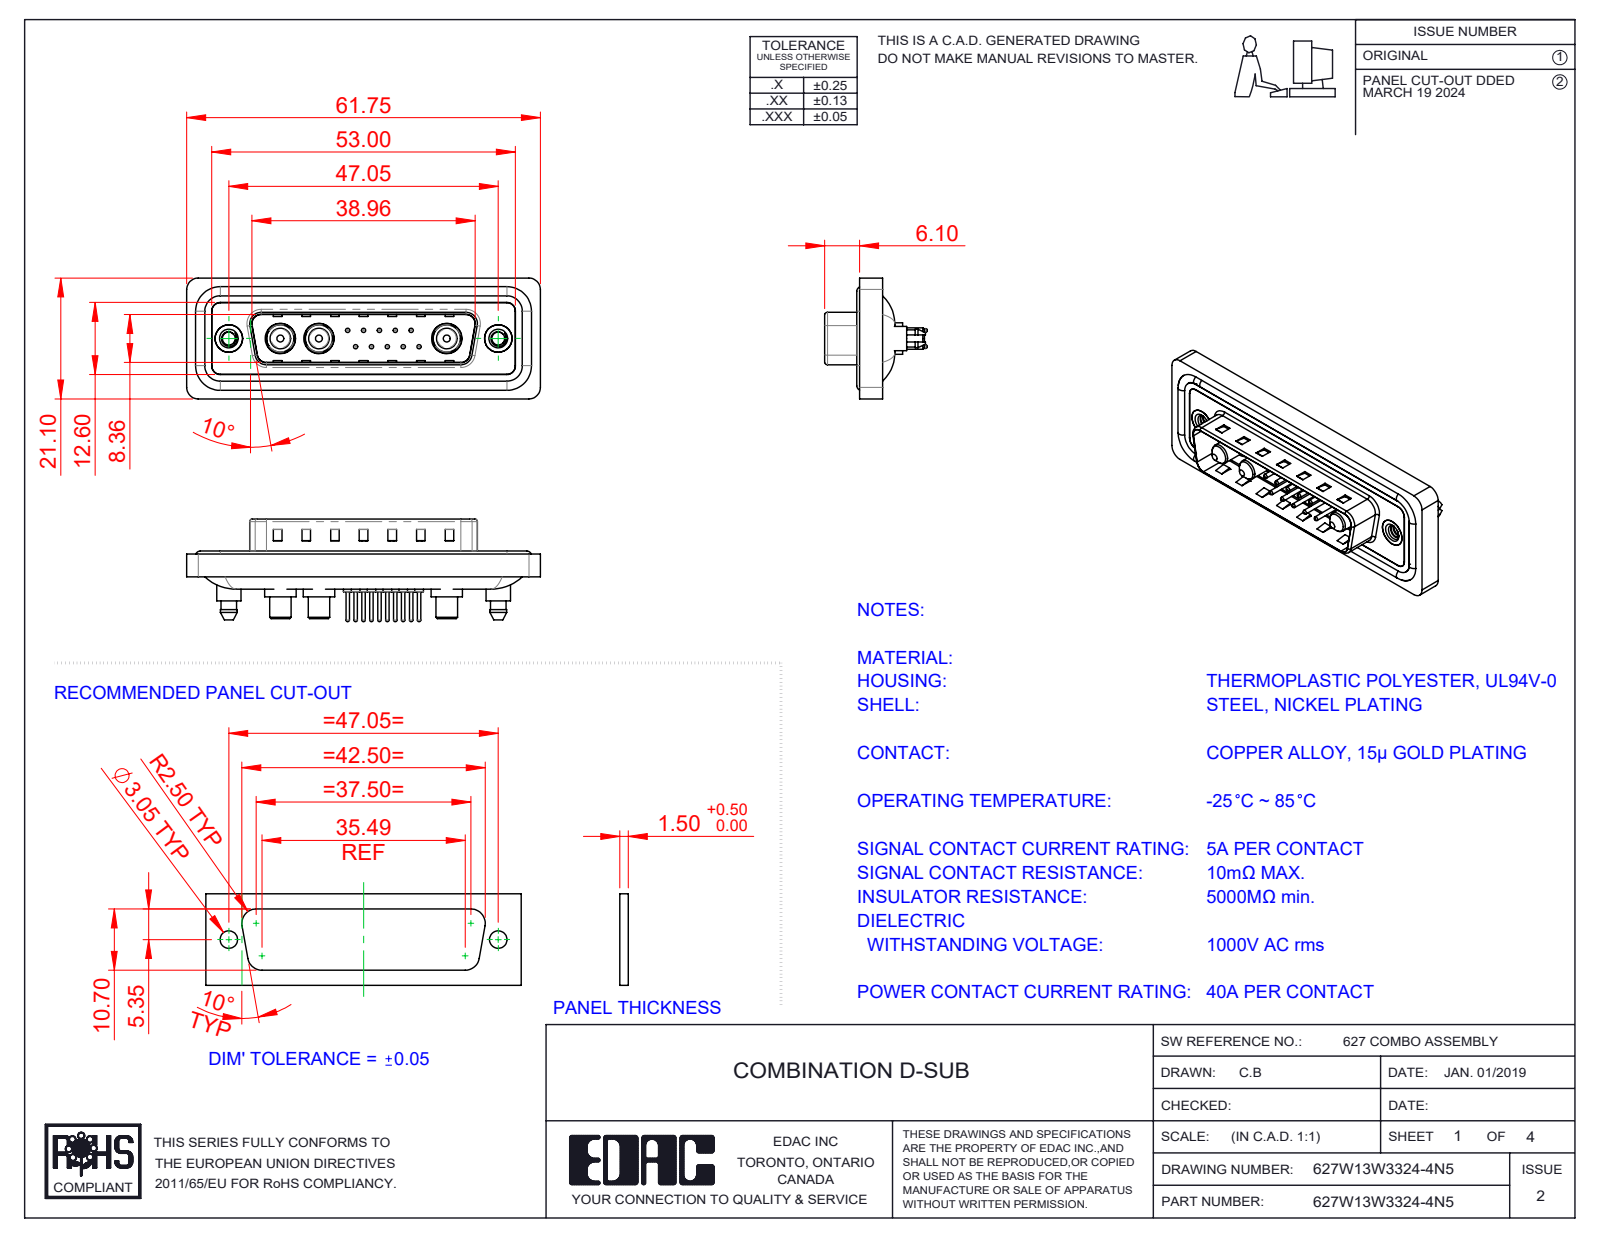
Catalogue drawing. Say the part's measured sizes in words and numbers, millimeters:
The part is named "627Combo Waterproof Housing_25 Contacts; 627W13W3324-4N5; 627Combo Housing_13W3; 627Combo Threaded Boardlock_5 (+5 more)". Its 3-D file was written by "SolidWorks 2023 (CONFIG_CONTROL_DESIGN)". It is 23 solids with 1020 faces: 325 planar, 417 cylindrical and 278 other. Overall it measures 61.75 by 21.1 by 17.9 millimeters. Its volume is 7 524 cubic millimeters and its surface area 12 240 square millimeters. Round holes: 10 of diameter 0.75, 10 of diameter 1.6, 10 of diameter 2, 3 of diameter 4.85, 3 of diameter 5.3, 2 of diameter 2.26, 2 of diameter 4, 2 of diameter 4.8, 2 of diameter 5. Round bosses or shafts: 10 of diameter 1.5, 10 of diameter 0.6, 4 of diameter 1.6, 3 of diameter 5.5, 3 of diameter 5.2, 3 of diameter 4.75, 3 of diameter 3.75, 3 of diameter 3.6. Partial cylindrical surfaces (rounded edges, fillets, slot ends): 24 of radius 1.5, 18 of radius 2, 10 of radius 1.6, 8 of radius 0.5, 4 of radius 0.25, 4 of radius 0.6, 4 of radius 0.65, 4 of radius 0.9. The main face-to-face distances are 0.4, 1.5, 1.1, 1.6, 0.5, 3.1, 2.9, 0.82, 9.58, 4.1. The hole center spacings are 3.16, 2.77, 5.04, 5.54, 7.49, 5.03, 8.31, 10.11.
